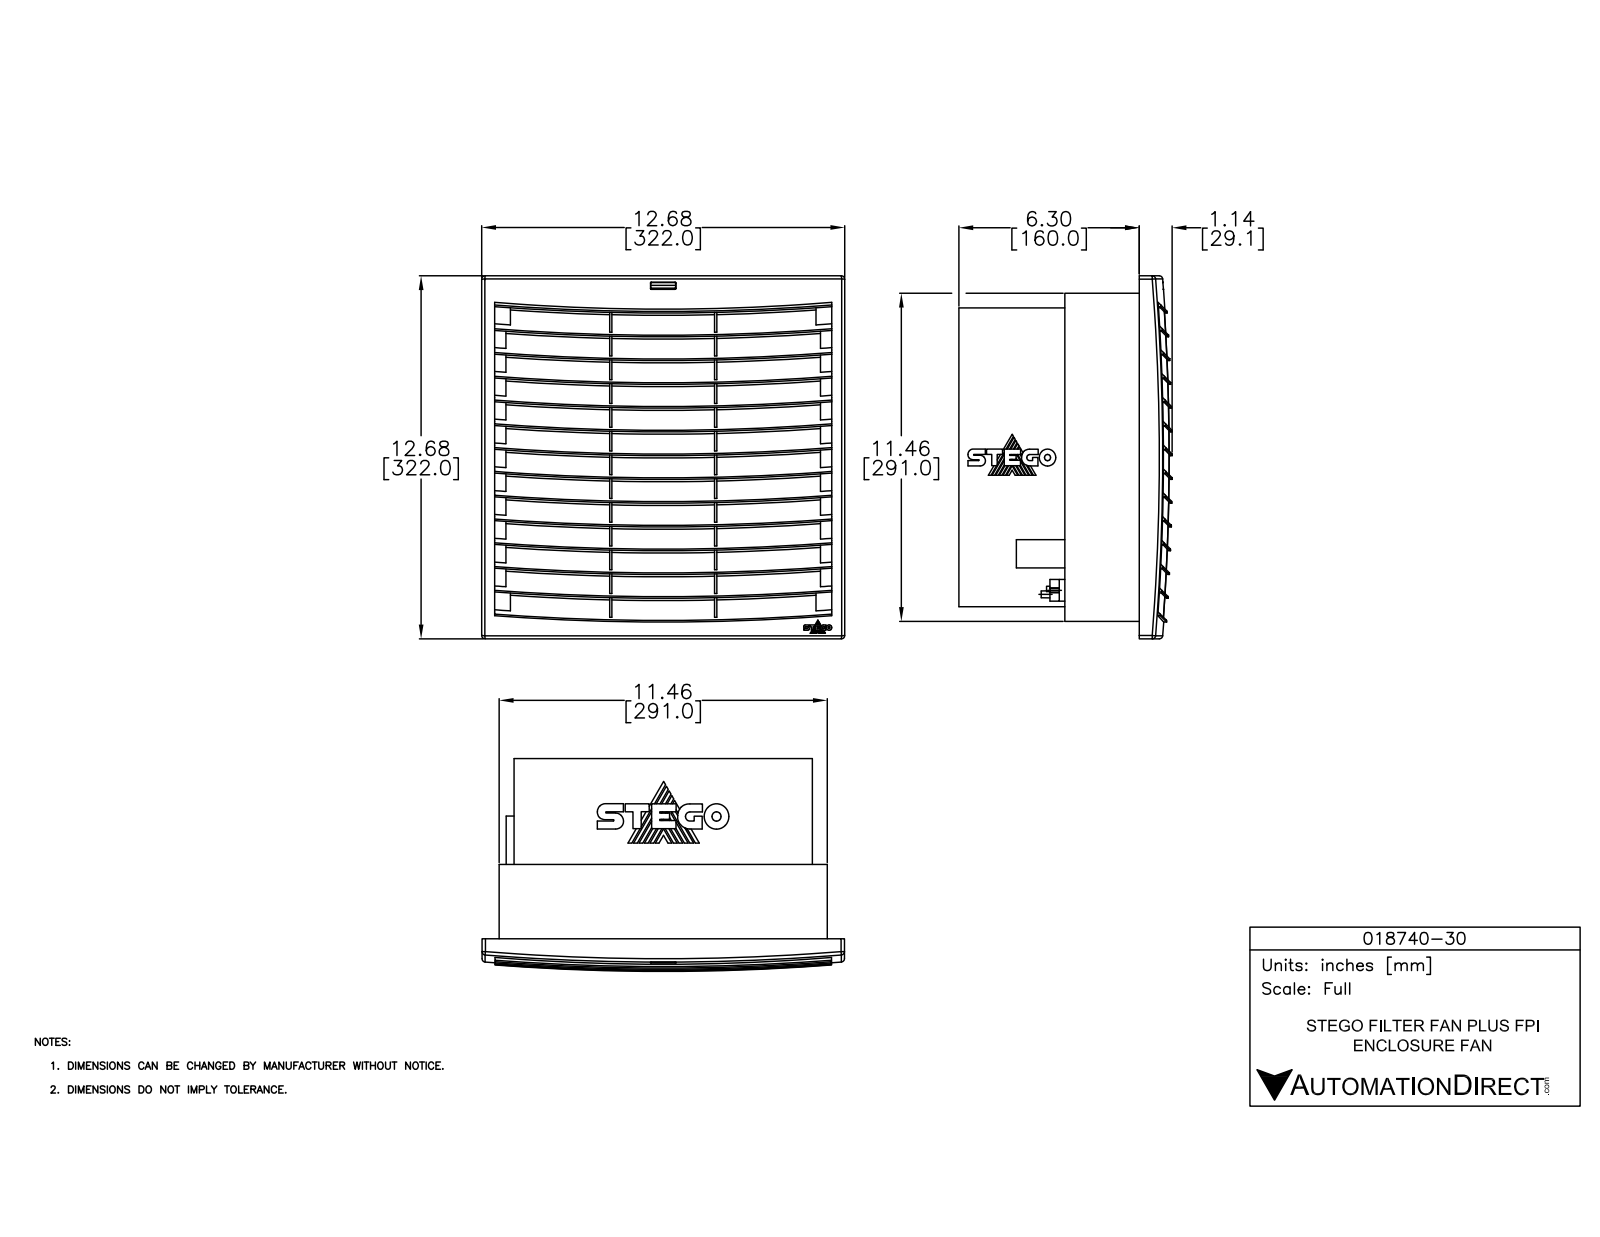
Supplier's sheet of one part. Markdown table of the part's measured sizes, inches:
| quantity | value |
| --- | --- |
| part name | 018740-30 |
| STEP written by | SolidWorks 2018 (AUTOMOTIVE_DESIGN) |
| units | inches |
| bodies | 1 solid, 837 faces (483 planar, 354 cylindrical, 0 other) |
| overall size | 12.677 × 12.677 × 7.441 |
| volume | 346.7 in³ |
| surface area | 1 597 in² |
| round holes (diameter × count) | 3 × 1, 3.99 × 1, 4.692 × 1, 4.979 × 1, 5.909 × 1, 5.969 × 1, 6.958 × 1, 7.126 × 1, 7.947 × 1, 8.344 × 1, 9.134 × 1, 9.738 × 1 |
| round bosses / shafts (diameter × count) | 11.389 × 1, 10.846 × 1, 10.738 × 1, 8.698 × 1, 8.341 × 1, 7.481 × 1, 7.352 × 1, 6.362 × 1 |
| partial cylindrical surfaces (radius × count) | 64.96 × 23, 4.43 × 7, 0.276 × 4, 0.343 × 4, 1.217 × 1, 1.737 × 1, 1.914 × 1, 44.216 × 1 |
| main face-to-face distances | 0.636, 1.272, 1.909, 0.591, 2.545, 0.197, 3.181, 0.059, 0.287, 11.17 |
